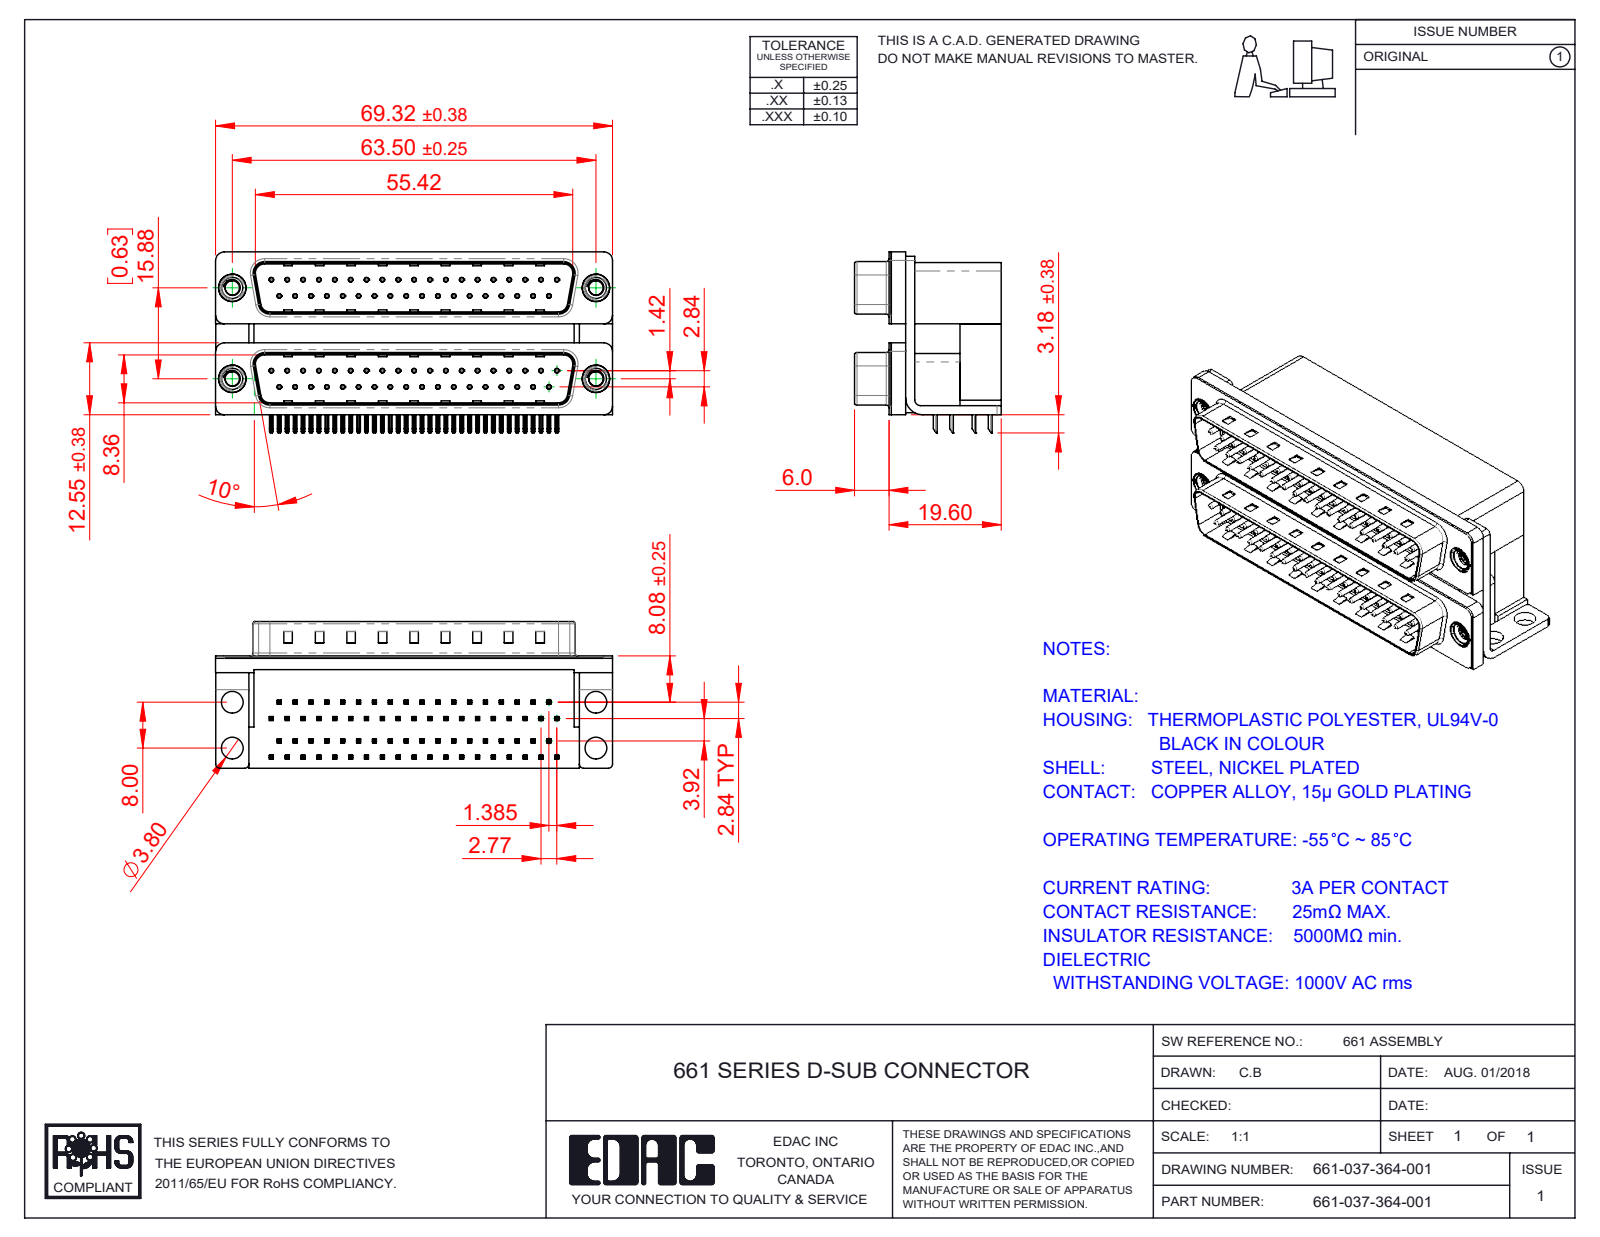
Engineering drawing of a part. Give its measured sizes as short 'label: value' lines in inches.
name: 661 Mounting Bracket_NoneL; 661 Contact Bottom Upper_L; 661 Contact Bottom Lower; 661 Shell_37 Contacts (+7 more)
written by: SolidWorks 2020 (CONFIG_CONTROL_DESIGN)
unit: in
bodies: 85 solids, 6586 faces (4250 planar, 1802 cylindrical, 534 other)
size: 2.729 × 1.244 × 1.008
volume: 1.703 in³; area: 44.21 in²
holes: 74× ⌀0.014, 74× ⌀0.031, 4× ⌀0.098, 4× ⌀0.138, 4× ⌀0.15, 4× ⌀0.157, 4× ⌀0.189, 4× ⌀0.197
bosses: 74× ⌀0.03, 4× ⌀0.193, 4× ⌀0.187, 4× ⌀0.154
rounds: 296× R0.01, 148× R0.005, 16× R0.02, 13× R0.059, 8× R0.03, 8× R0.035, 8× R0.063, 8× R0.079
face distances: 0.016, 0.756, 0.625, 0.283, 0.472, 0.421, 0.345, 0.611, 1.032, 0.086
hole spacings: 0.109, 0.218, 0.124, 0.327, 0.436, 0.545, 0.654, 0.763
